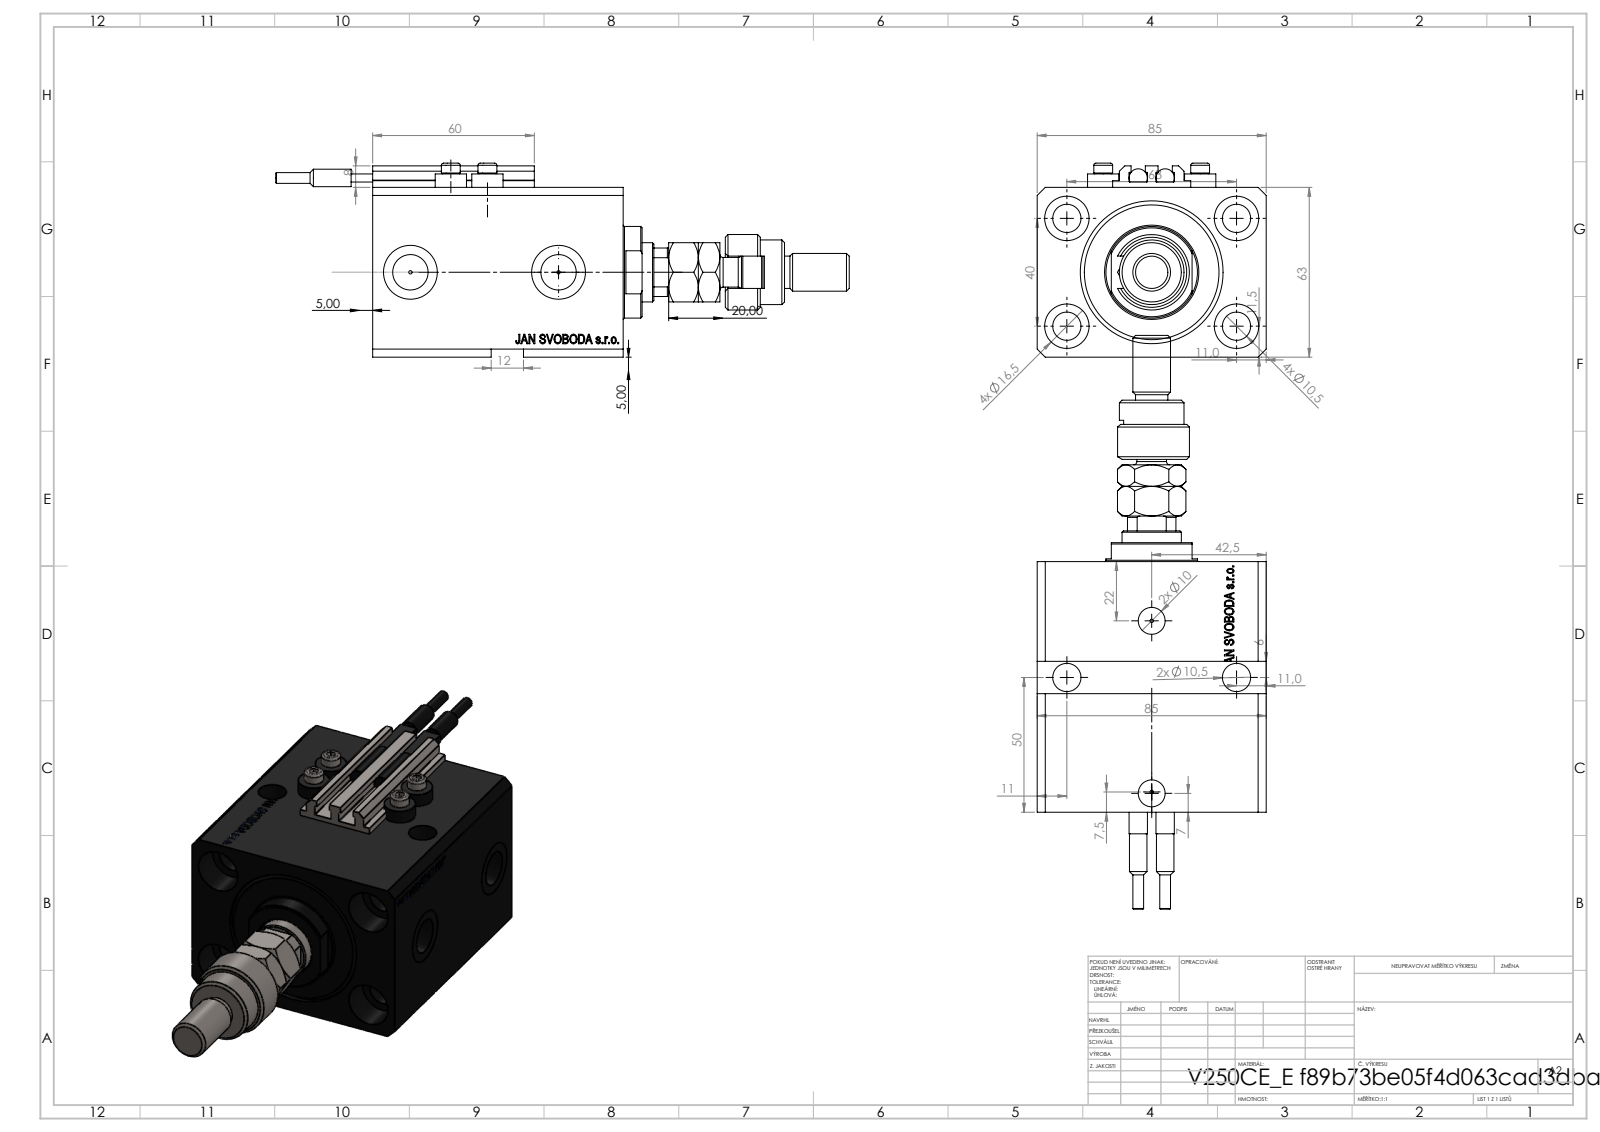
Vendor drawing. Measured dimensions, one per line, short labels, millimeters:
name: FEMALE_PART_FOR_DFA; SWITCH_V250CE; ALLEN BOLT V250CE; MFA (+3 more)
written by: SolidWorks 2019 (CONFIG_CONTROL_DESIGN)
unit: mm
bodies: 12 solids, 1240 faces (599 planar, 163 cylindrical, 478 other)
size: 213 × 85 × 72
volume: 459 118 mm³; area: 107 655 mm²
holes: 6× ⌀10.5, 4× ⌀1.25, 4× ⌀4, 4× ⌀16.5, 2× ⌀10, 2× ⌀13.16, 2× ⌀20, 1× ⌀12.5, 1× ⌀22, 1× ⌀40, 1× ⌀53
bosses: 4× ⌀11.6, 4× ⌀7, 2× ⌀6.8, 2× ⌀6.5, 2× ⌀4, 1× ⌀34, 1× ⌀28, 1× ⌀24
rounds: 10× R0.2, 1× R9.75, 1× R10.5
face distances: 63, 85, 93, 17, 76, 11.4, 64.6, 81.6, 3, 65
hole spacings: 37.31, 63, 13.6, 15.4, 24.96, 28.02, 28.43, 33.62
